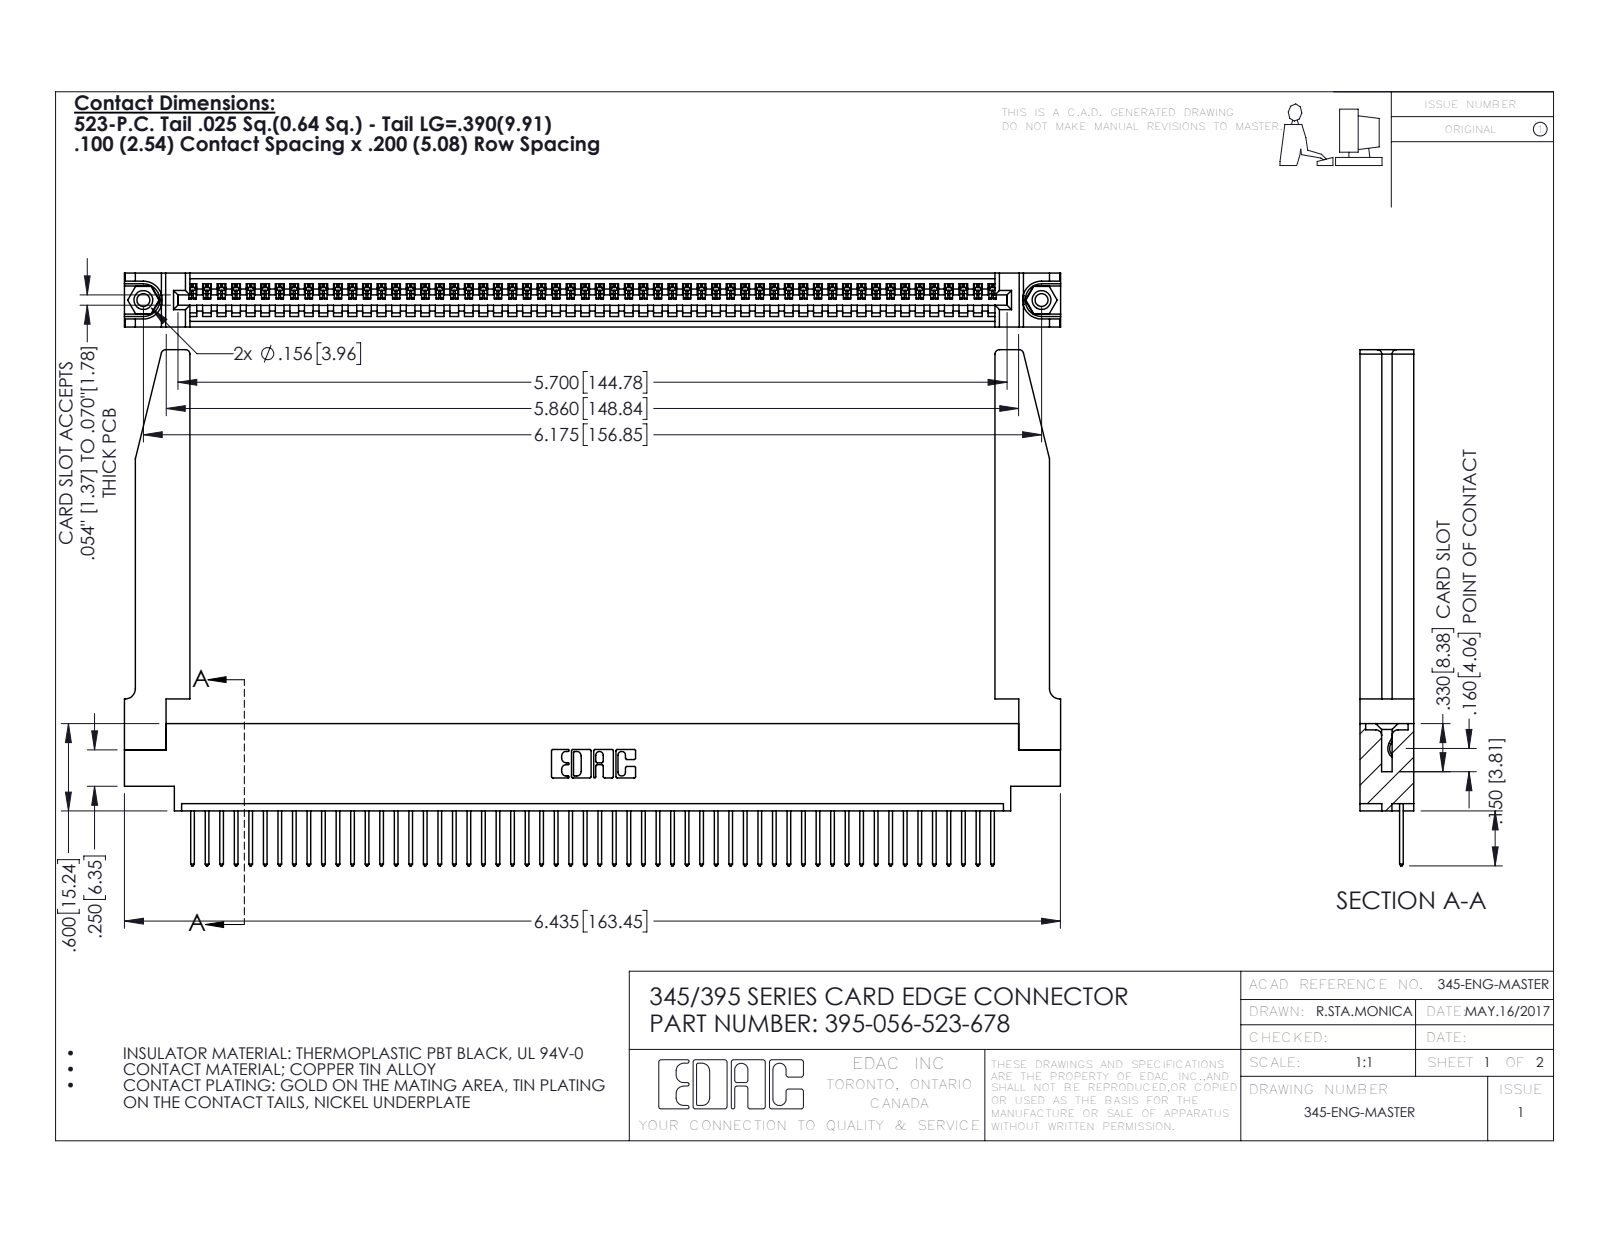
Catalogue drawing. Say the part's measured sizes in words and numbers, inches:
The part is named "345 Part_0.170 Offset - 0.156 Dia-TH; 395-056-523-678; 345-292-001_345-293-123; 345-250-001_345-250-001-102 (+1 more)". Its 3-D file was written by "SolidWorks 2016 (CONFIG_CONTROL_DESIGN)". It is 61 solids with 3612 faces: 2466 planar, 1094 cylindrical and 52 other. Overall it measures 6.436 by 3.547 by 0.37 inches. Its volume is 1.42 cubic inches and its surface area 43.14 square inches. Round holes: 2 of diameter 0.089, 2 of diameter 0.125, 2 of diameter 0.156, 1 of diameter 0.064. Round bosses or shafts: 2 of diameter 0.155. Partial cylindrical surfaces (rounded edges, fillets, slot ends): 112 of radius 0.006, 112 of radius 0.01, 22 of radius 0.01, 8 of radius 0.03, 6 of radius 0.007, 6 of radius 0.031, 3 of radius 0.026, 2 of radius 0.031. The main face-to-face distances are 0.37, 0.072, 0.298, 0.098, 0.272, 0.025, 0.2, 0.225, 0.148, 0.15. The hole center spacings are 0.27, 5.939, 6.175.
